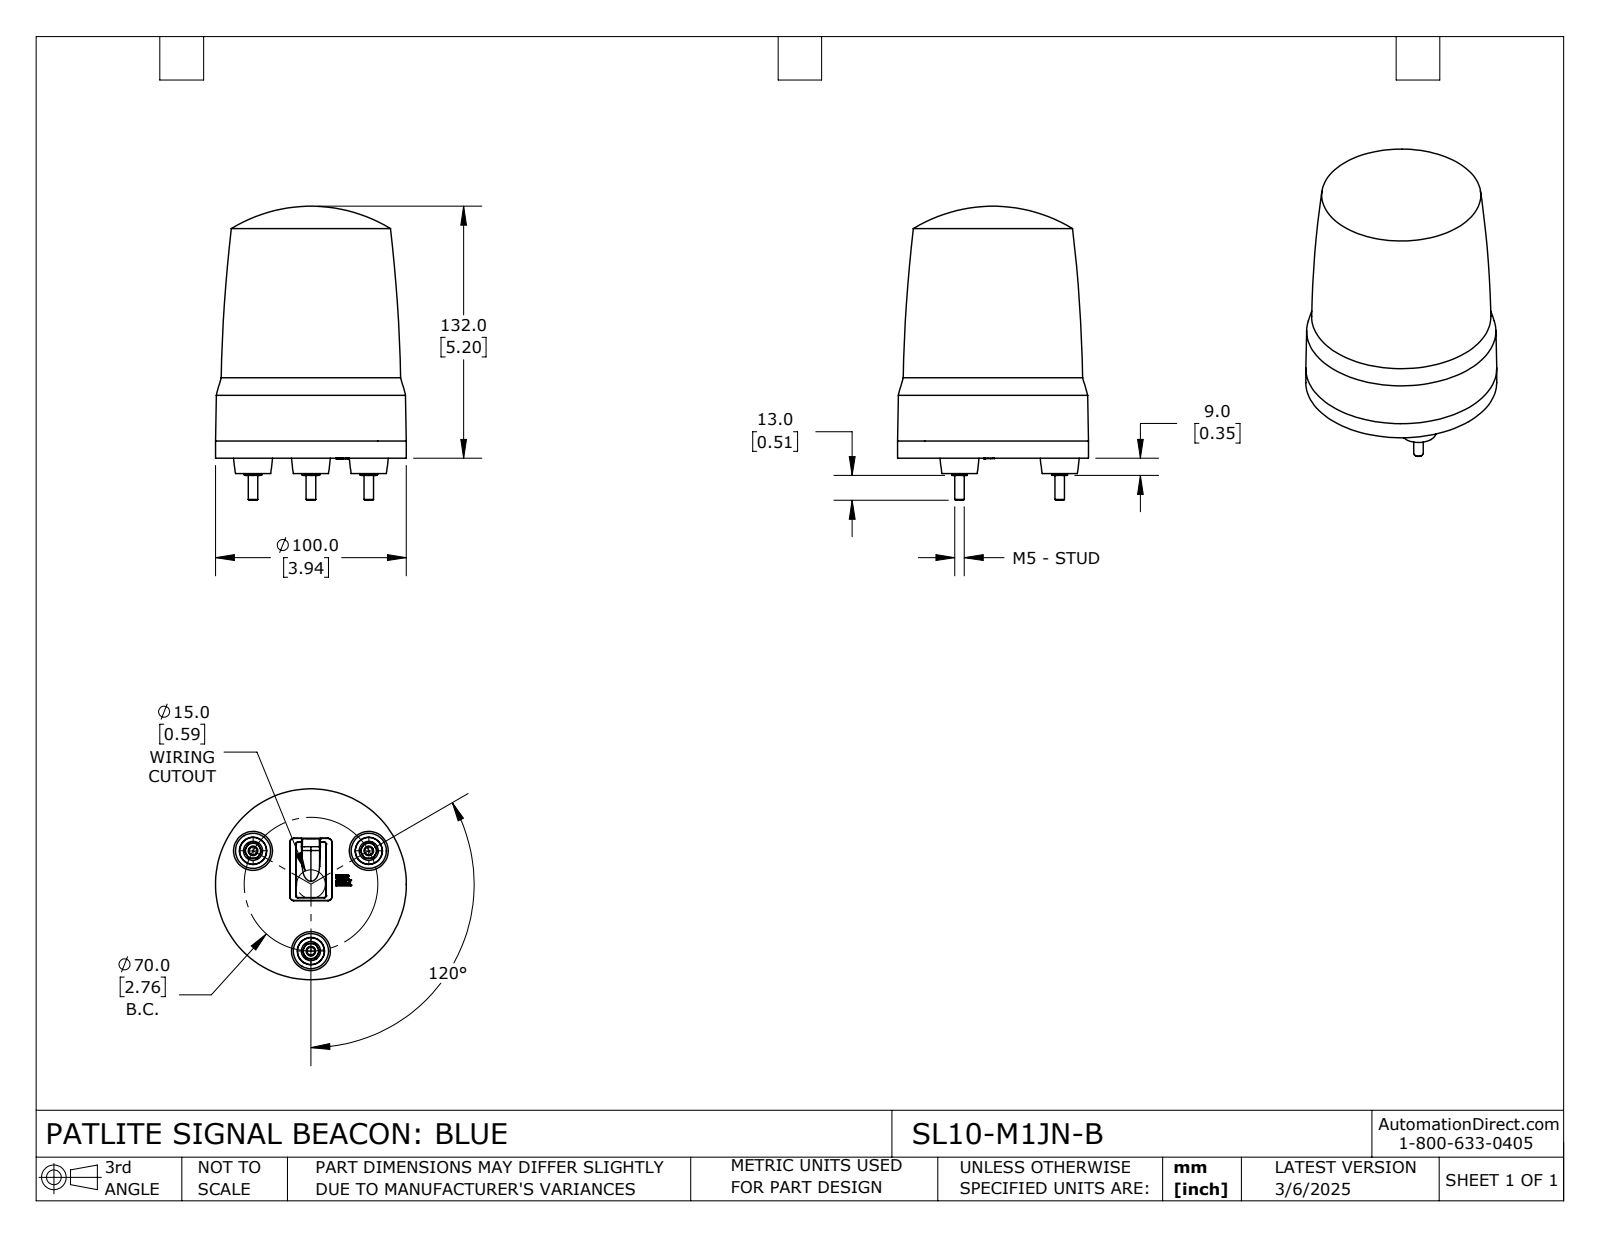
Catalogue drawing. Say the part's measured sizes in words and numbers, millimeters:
The part is named "SL10-M1JN-B". Its 3-D file was written by "SolidWorks 2024 (CONFIG_CONTROL_DESIGN)". It is 1 solid with 327 faces: 159 planar, 14 cylindrical and 154 other. Overall it measures 154 by 100 by 100 millimeters. Its volume is 859 960 cubic millimeters and its surface area 52 586 square millimeters. Round bosses or shafts: 3 of diameter 10, 3 of diameter 5, 1 of diameter 100. The main face-to-face distances are 8, 0.85, 8.85, 1.6, 10.45, 2.45, 3.8, 4.2, 5.05, 6.65.
